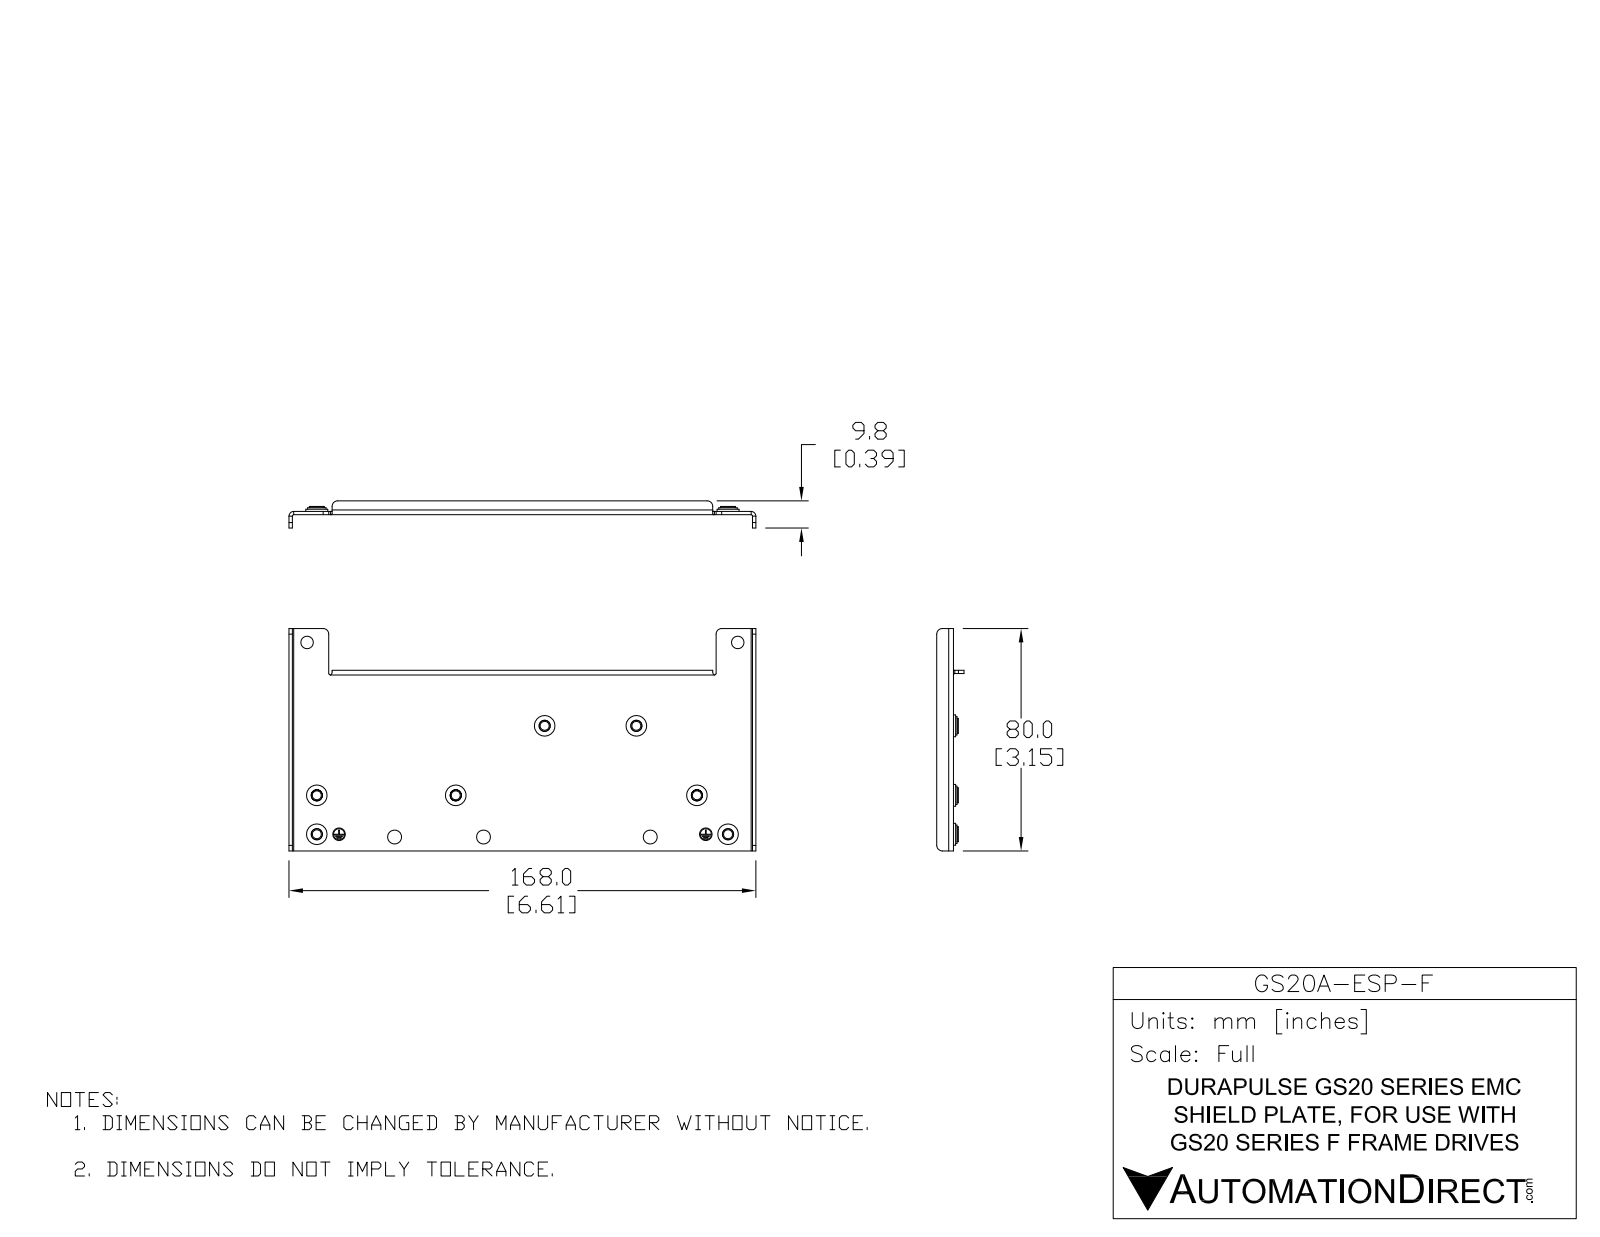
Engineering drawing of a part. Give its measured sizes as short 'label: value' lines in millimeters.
name: MKM-EPF-PD-3D00 r1
written by: SolidWorks 2017 (AUTOMOTIVE_DESIGN)
unit: mm
bodies: 15 solids, 604 faces (223 planar, 161 cylindrical, 220 other)
size: 168 × 80 × 36.7
volume: 24 270 mm³; area: 45 230 mm²
holes: 7× ⌀3.3, 7× ⌀5.4, 5× ⌀6.5, 3× ⌀5, 2× ⌀4.5, 2× ⌀8
bosses: 7× ⌀7.9, 7× ⌀5.4, 5× ⌀6.6, 2× ⌀8, 2× ⌀7.2, 2× ⌀6.9, 2× ⌀6.6, 2× ⌀4
rounds: 10× R2.7, 10× R7.5, 8× R0.5, 6× R2, 5× R10.1, 5× R11.1, 3× R1.7
face distances: 1.2, 1, 2.2, 25, 166.8, 52.5, 32.5, 57.5, 27.4, 65
hole spacings: 9, 19, 28, 69.1, 70.1, 76.8, 111, 120
